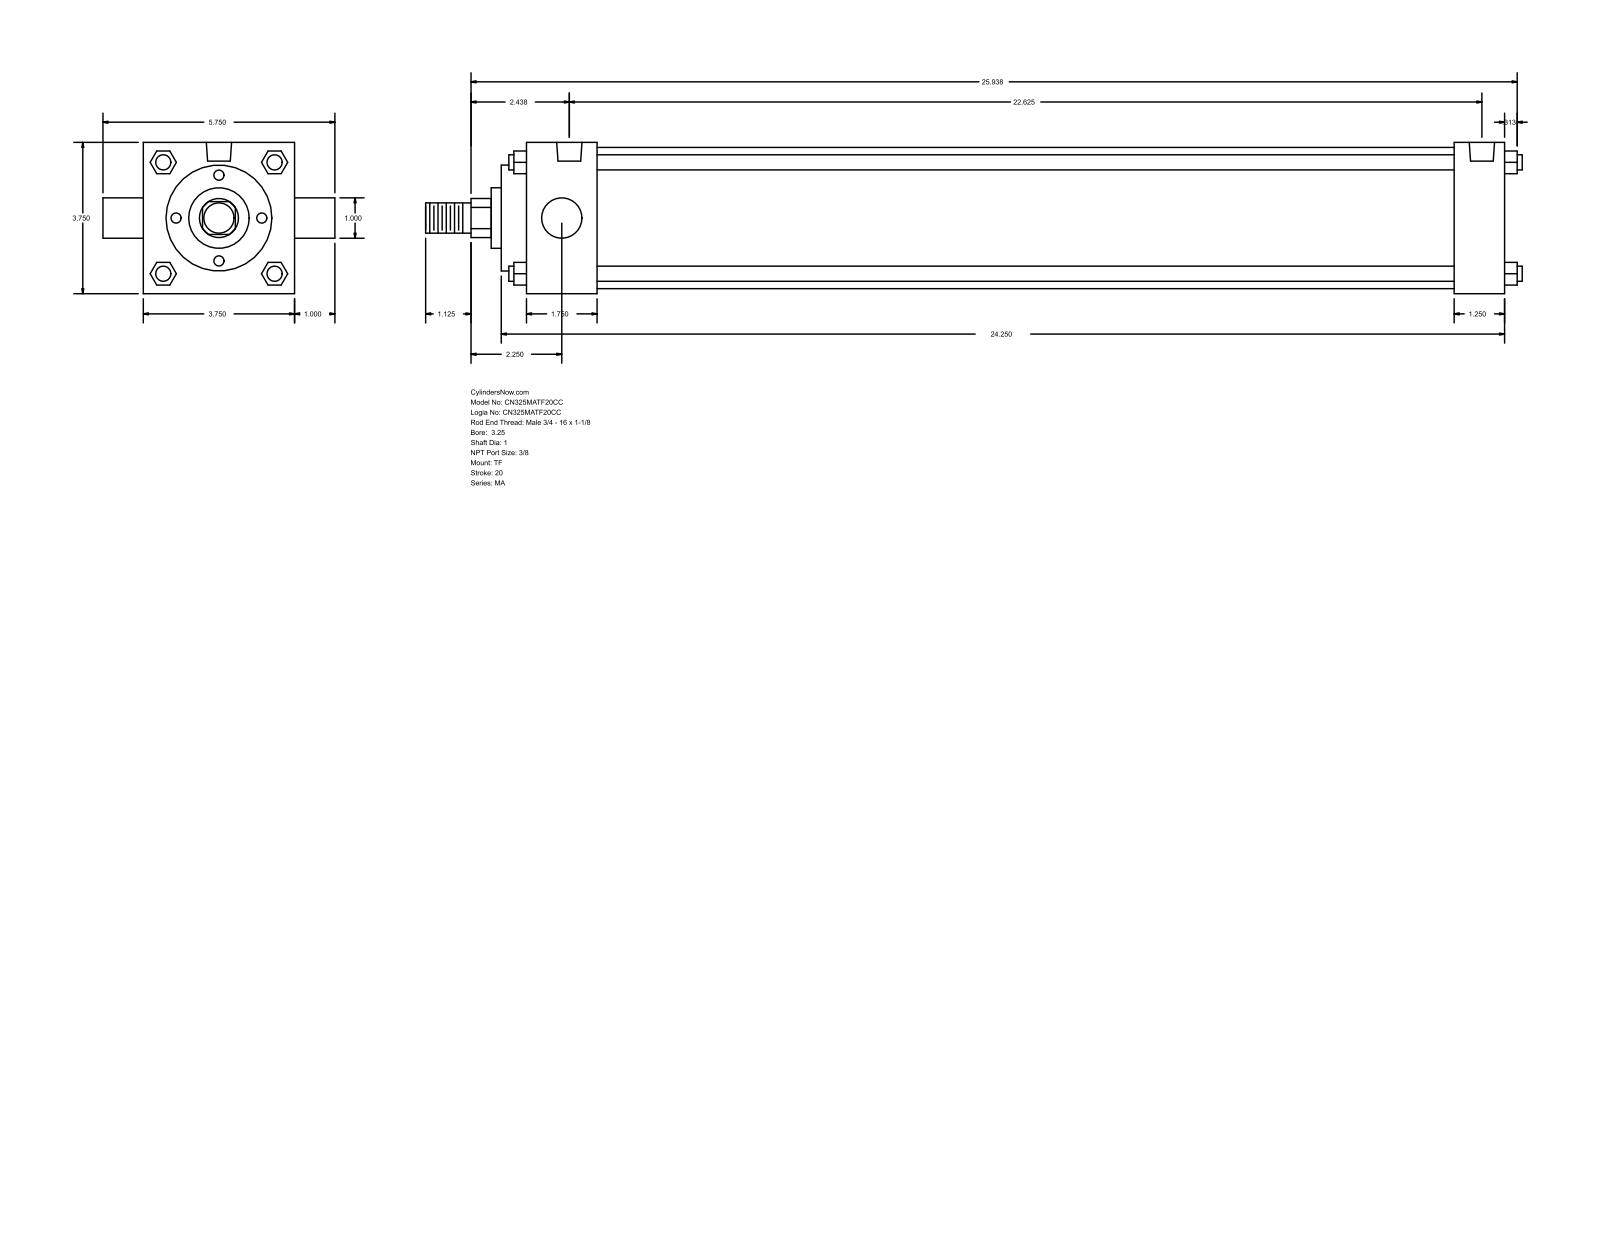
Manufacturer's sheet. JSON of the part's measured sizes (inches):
{"part_name": "MA_TF__0325_1", "step_written_by": "GSSL Pune (CONFIG_CONTROL_DESIGN)", "units": "inches", "bodies": {"solids": 0, "faces": 122, "planar": 93, "cylindrical": 29, "other": 0}, "overall_size": [27.187, 5.75, 3.75], "round_holes": [[0.437, 3], [0.627, 2]], "round_bosses_or_shafts": [[0.375, 4], [1, 2], [3.5, 1], [2.625, 1], [1.5, 1], [0.75, 1]], "partial_cylinders_radius": [[0.484, 1]], "face_to_face_distances": [3.75, 24.25, 1.75, 23, 21.25, 22.5, 1.25, 0.625, 2.375, 23.625], "hole_center_spacings": [0.187, 22.438, 22.25, 22.625]}
